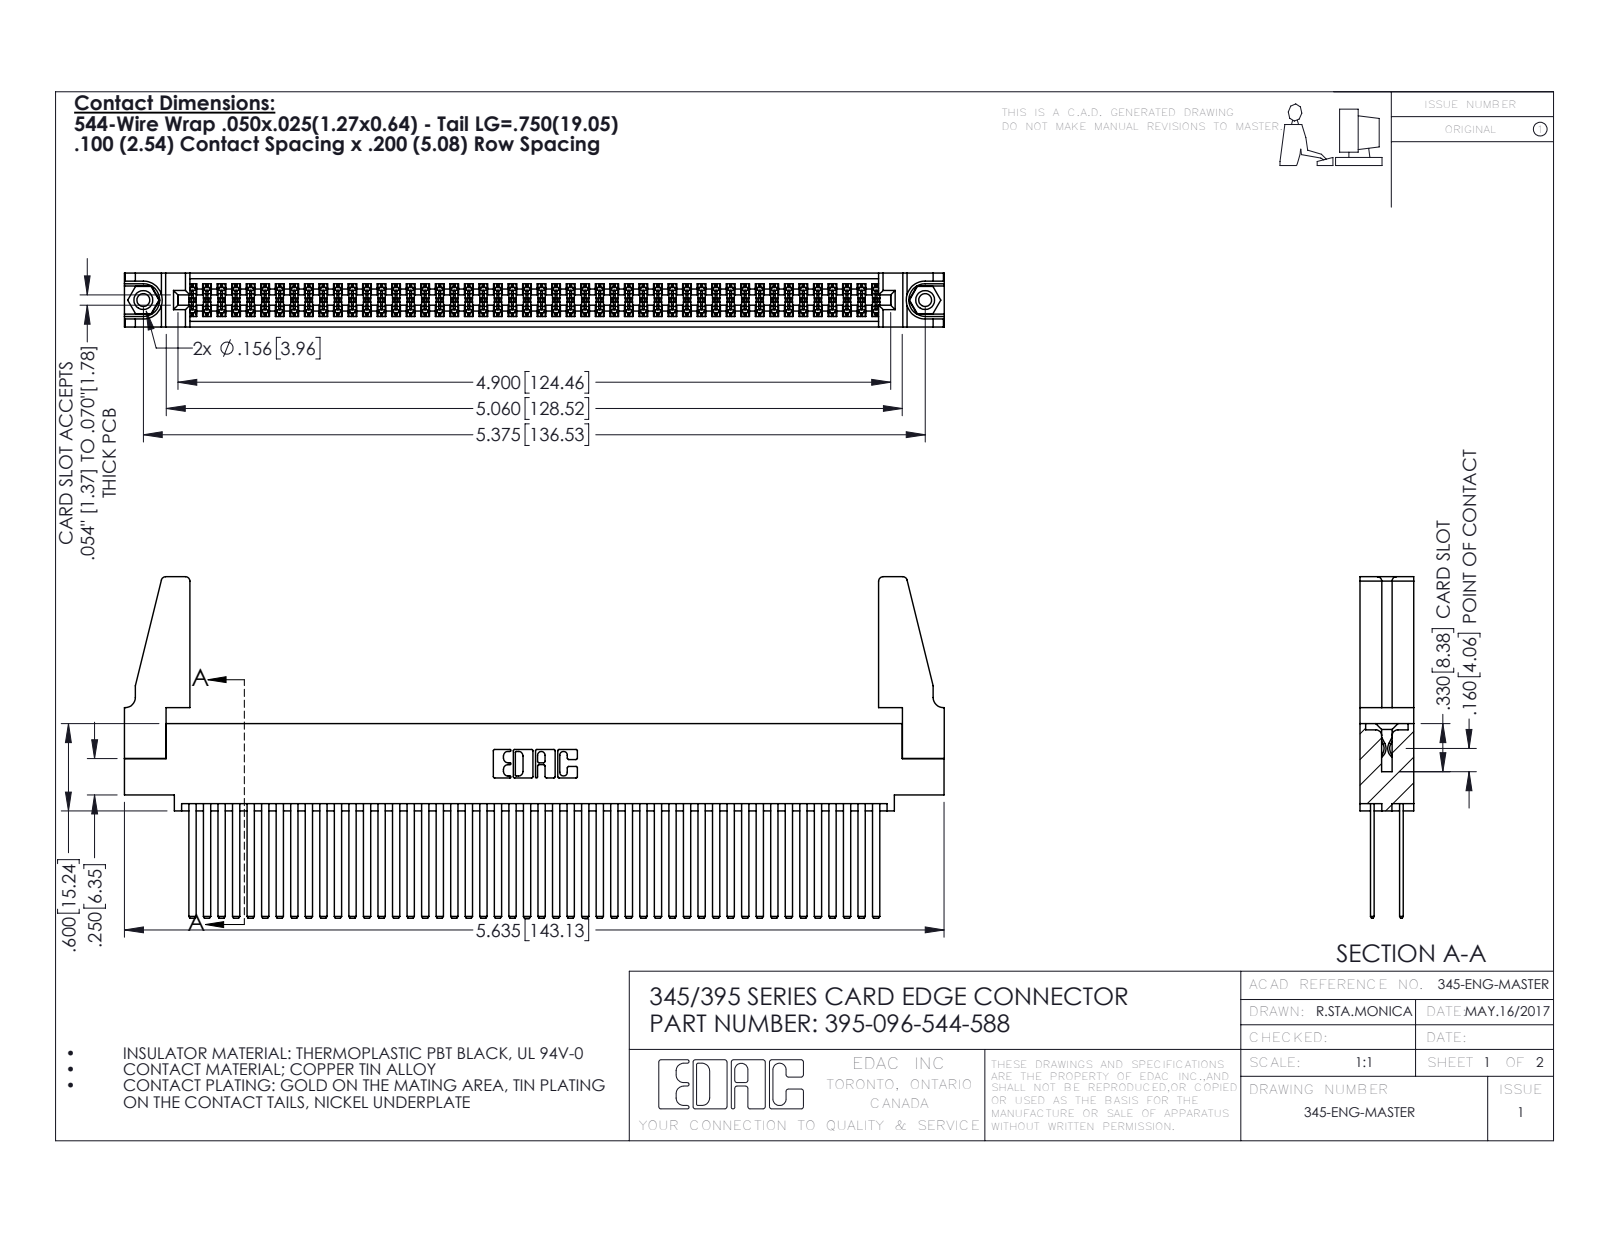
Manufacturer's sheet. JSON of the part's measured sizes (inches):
{"part_name": "345-250-001_345-250-001-102; 345-220-078_345-220-088; 395-096-544-588; 345 Part_0.110 Offset - 0.156 Dia-TH (+1 more)", "step_written_by": "SolidWorks 2016 (CONFIG_CONTROL_DESIGN)", "units": "inches", "bodies": {"solids": 101, "faces": 4478, "planar": 2940, "cylindrical": 1522, "other": 16}, "overall_size": [5.636, 2.347, 0.37], "volume_in3": 1.128, "surface_area_in2": 46.18, "round_holes": [[0.089, 2], [0.125, 2], [0.156, 2], [0.064, 1]], "round_bosses_or_shafts": [[0.155, 2]], "partial_cylinders_radius": [[0.006, 144], [0.01, 22], [0.03, 8], [0.007, 6], [0.031, 6], [0.026, 3], [0.014, 2], [0.019, 2]], "face_to_face_distances": [0.072, 0.298, 0.2, 0.098, 0.272, 0.025, 0.225, 0.37, 0.175, 0.149], "hole_center_spacings": [0.27, 5.139, 5.375]}
